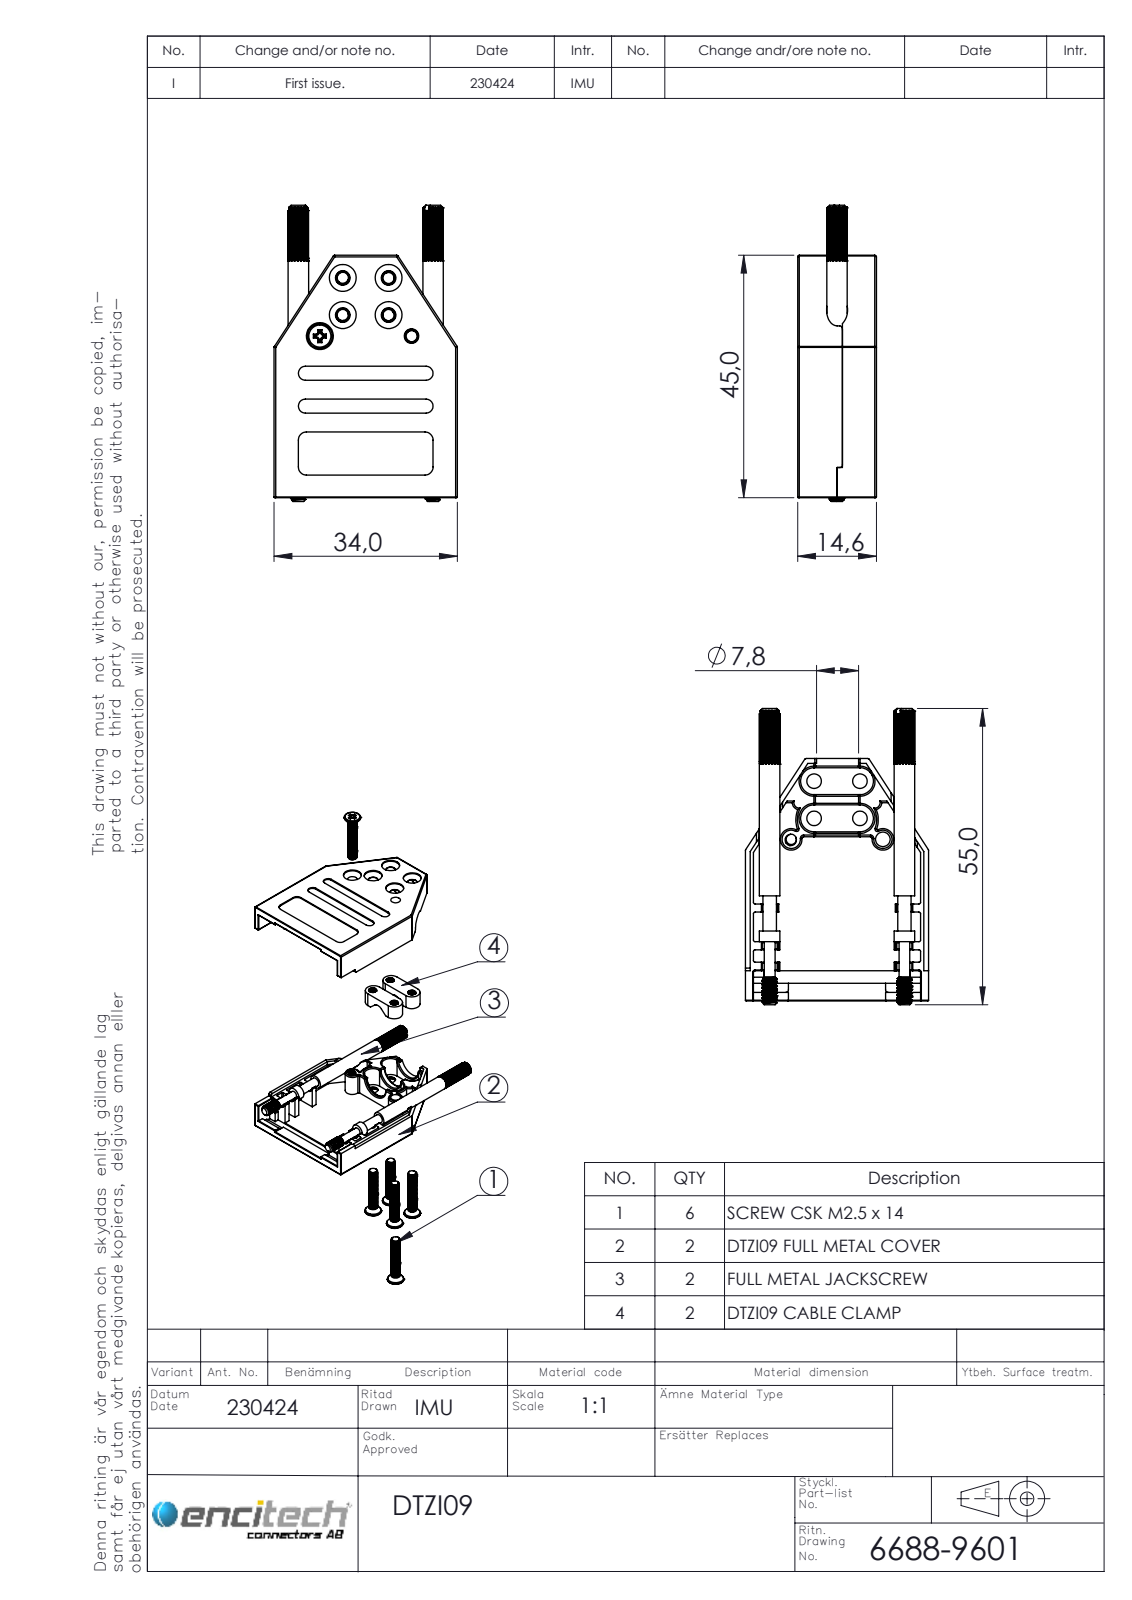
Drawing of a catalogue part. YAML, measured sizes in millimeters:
part_name: "6826-0143-02; 6855-0117-10; 6805-0305-01; 6688-9601 (+1 more)"
step_written_by: "SolidWorks 2021 (AUTOMOTIVE_DESIGN)"
units: millimeters
bodies: {solids: 12, faces: 1694, planar: 520, cylindrical: 800, other: 374}
overall_size: [54.5, 34, 14.6]
volume: 7764
surface_area: 13263
round_holes:
  - {diameter: 2.7, count: 6}
  - {diameter: 5, count: 6}
  - {diameter: 2.05, count: 4}
  - {diameter: 1.9, count: 2}
  - {diameter: 2.8, count: 2}
  - {diameter: 3.9, count: 2}
  - {diameter: 8, count: 1}
round_bosses_or_shafts:
  - {diameter: 2.5, count: 8}
  - {diameter: 4.6, count: 6}
  - {diameter: 4, count: 2}
  - {diameter: 3.8, count: 2}
  - {diameter: 2.85, count: 2}
  - {diameter: 2, count: 2}
partial_cylinders:
  - {radius: 0.3, count: 44}
  - {radius: 0.15, count: 36}
  - {radius: 0.5, count: 12}
  - {radius: 0.25, count: 8}
  - {radius: 1.3, count: 4}
  - {radius: 1.5, count: 4}
  - {radius: 2.3, count: 4}
  - {radius: 1.3, count: 2}
face_to_face_distances: [13.4, 1.2, 1.5, 0.9, 14.6, 12.2, 14.3, 13.1, 7, 34]
hole_center_spacings: [5.77, 6.9, 8.5, 10.95, 11.61, 12.5, 13.33, 16.71]
